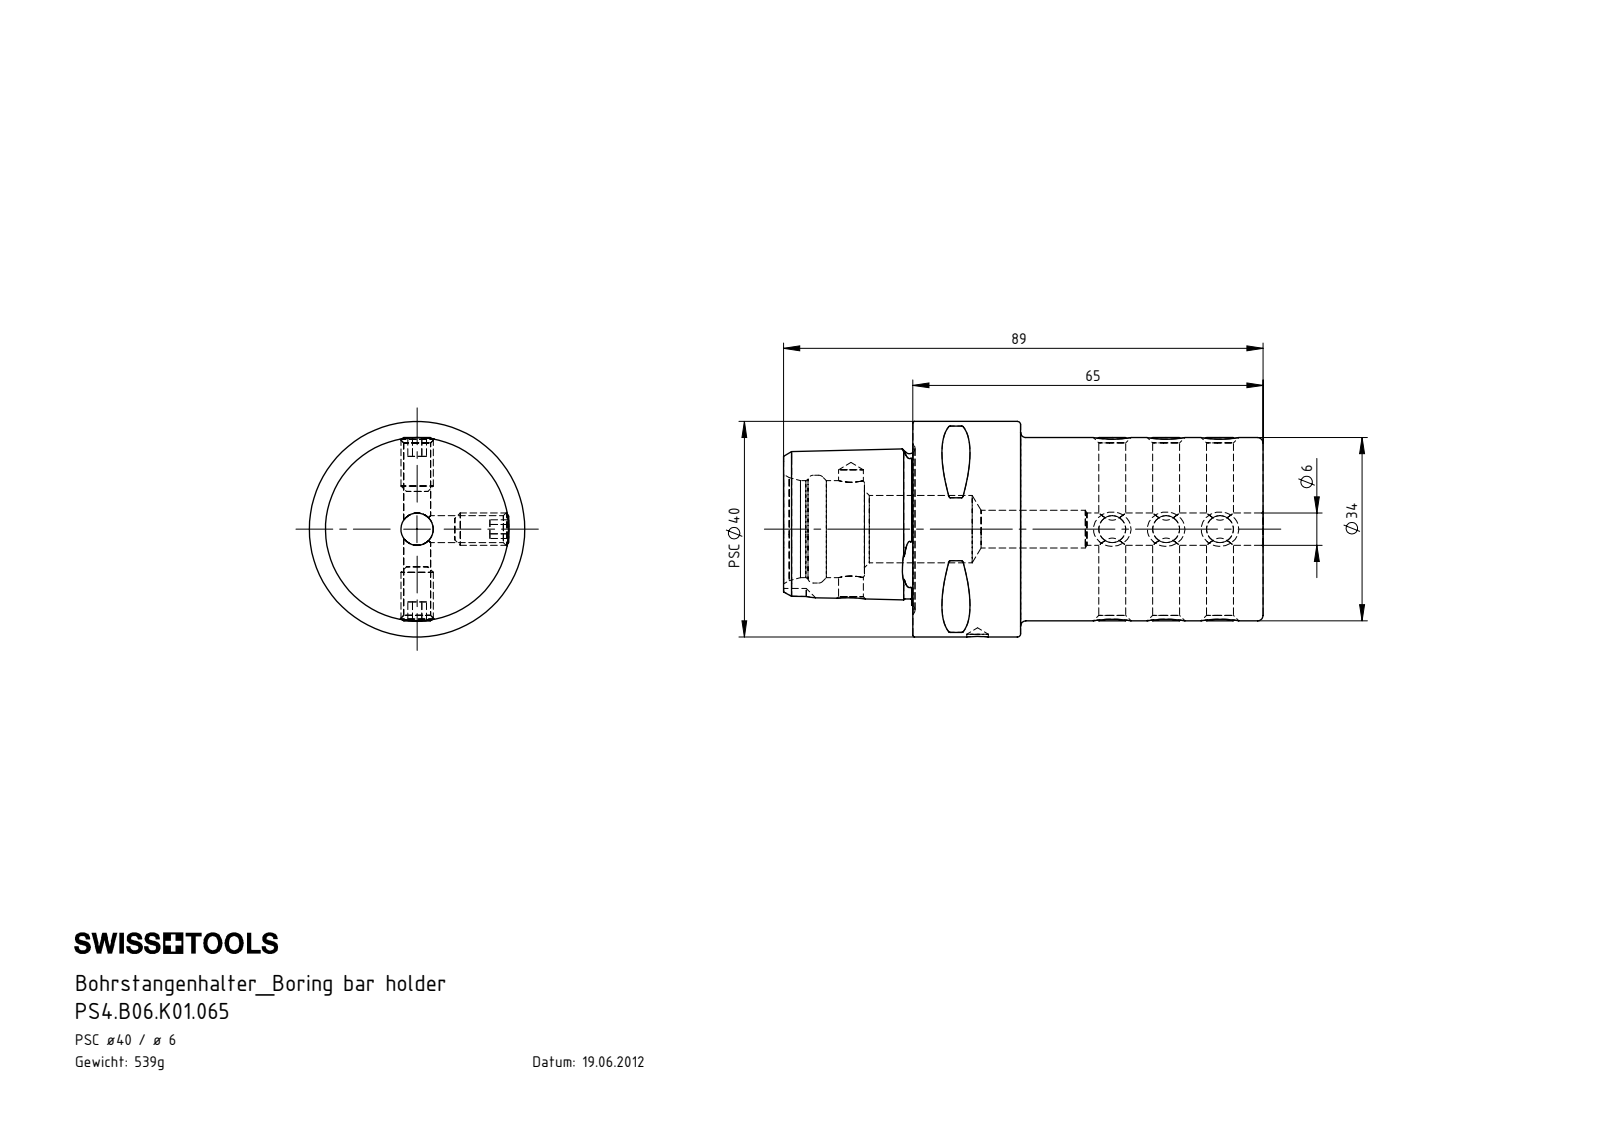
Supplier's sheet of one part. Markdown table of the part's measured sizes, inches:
| quantity | value |
| --- | --- |
| part name | PS4-B06.K01.065_A; PS4.B06.K01.065; ISO 4026 - M6 x 10_PreviewCfg |
| STEP written by | SolidWorks 2017 (AUTOMOTIVE_DESIGN) |
| units | inches |
| bodies | 10 solids, 315 faces (101 planar, 70 cylindrical, 144 other) |
| overall size | 3.504 × 1.575 × 1.575 |
| volume | 4.308 in³ |
| surface area | 28.68 in² |
| round holes (diameter × count) | 0.197 × 6, 0.157 × 1, 0.181 × 1, 0.236 × 1, 0.276 × 1, 0.492 × 1, 0.709 × 1, 0.787 × 1 |
| round bosses / shafts (diameter × count) | 0.236 × 6, 1.575 × 1, 1.339 × 1 |
| partial cylindrical surfaces (radius × count) | 0.012 × 8, 0.118 × 1 |
| main face-to-face distances | 2.559, 0.394, 0.945, 0.787, 1.772, 1.732, 3.504, 0.118, 0.197, 0.611 |
| hole center spacings | 0.394, 0.787, 0.925, 0.984, 1.378, 1.772, 1.909, 2.303 |
